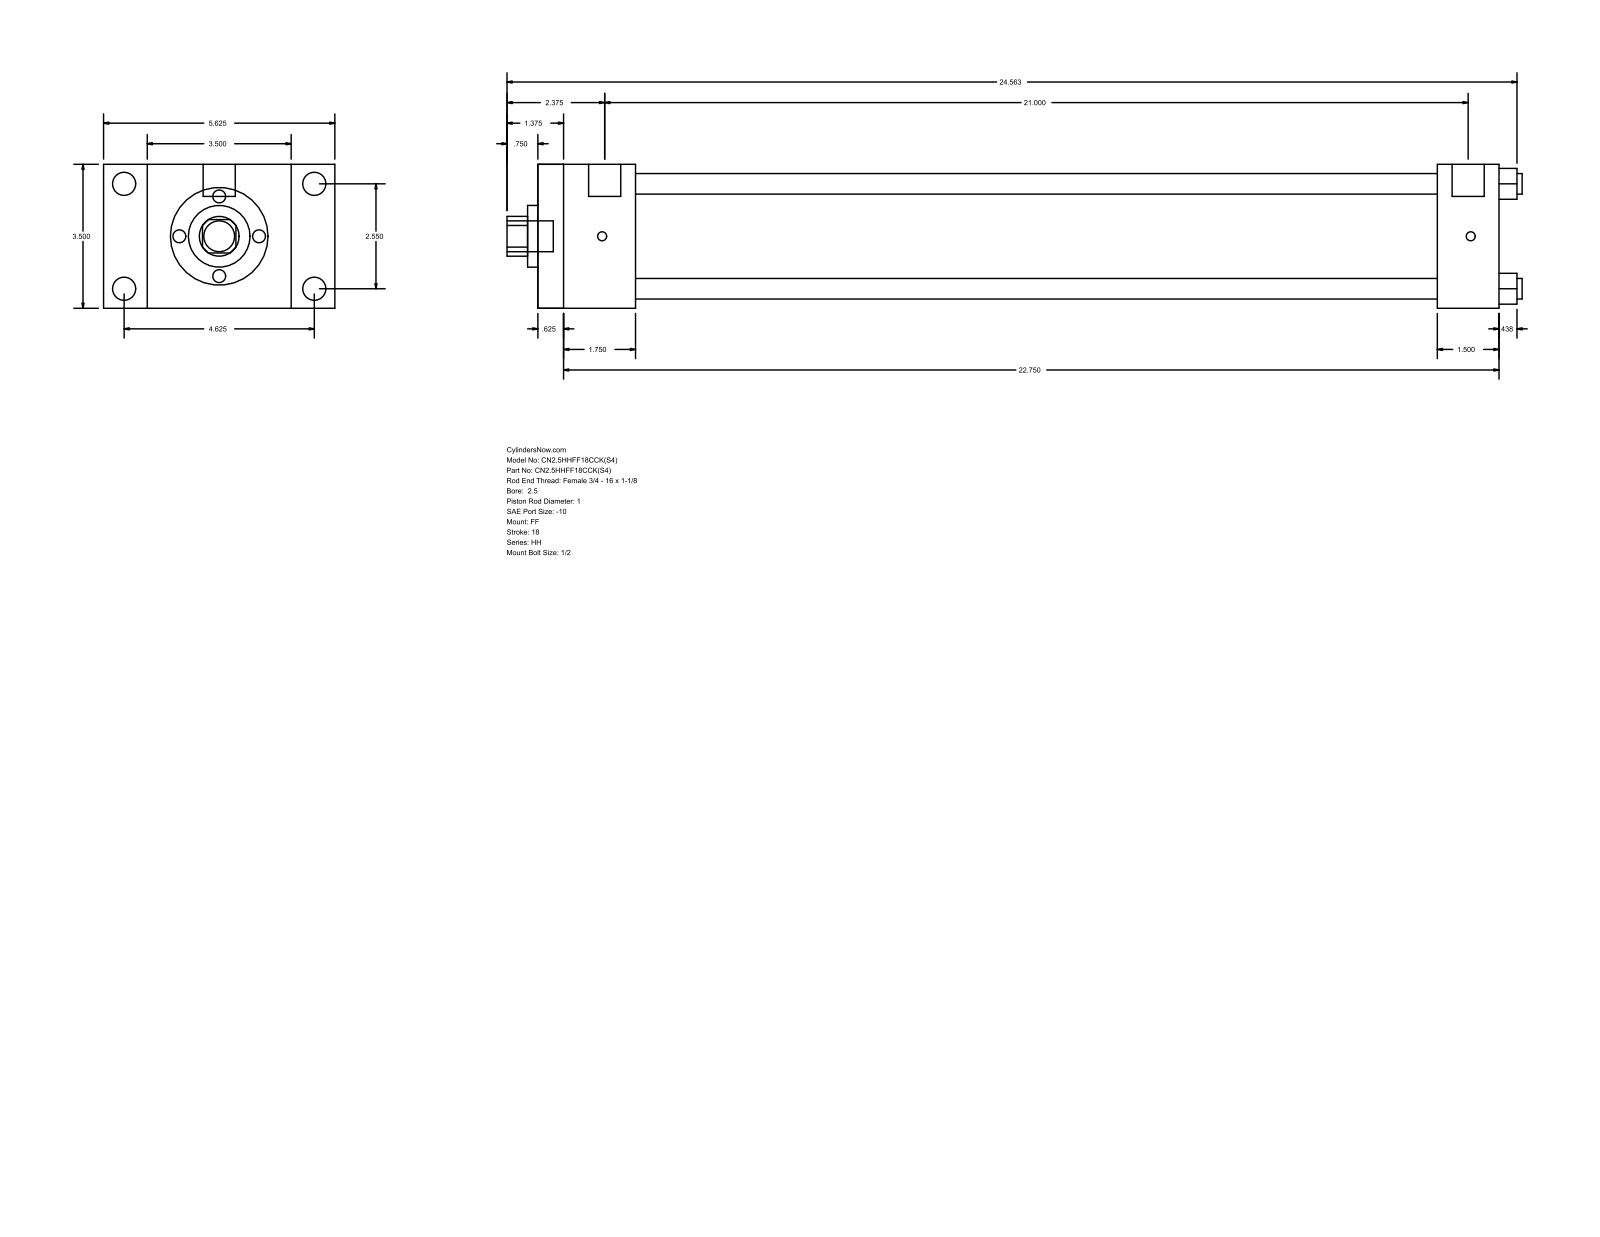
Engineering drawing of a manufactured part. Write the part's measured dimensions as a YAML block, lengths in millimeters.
part_name: "HH_FF__0250_1"
step_written_by: "GSSL Pune (CONFIG_CONTROL_DESIGN)"
units: millimeters
bodies: {solids: 0, faces: 92, planar: 64, cylindrical: 28, other: 0}
overall_size: [627.06, 142.88, 88.9]
round_holes:
  - {diameter: 12.7, count: 4}
  - {diameter: 25.4, count: 1}
  - {diameter: 38.1, count: 1}
  - {diameter: 73.03, count: 1}
round_bosses_or_shafts:
  - {diameter: 14.3, count: 4}
  - {diameter: 5.56, count: 4}
  - {diameter: 19.84, count: 2}
  - {diameter: 19.05, count: 1}
partial_cylinders:
  - {radius: 12.29, count: 1}
face_to_face_distances: [88.9, 593.72, 15.87, 577.85, 60.33, 44.46, 533.39, 555.62, 539.75, 495.29]
hole_center_spacings: [45.79, 64.76, 91.58]
